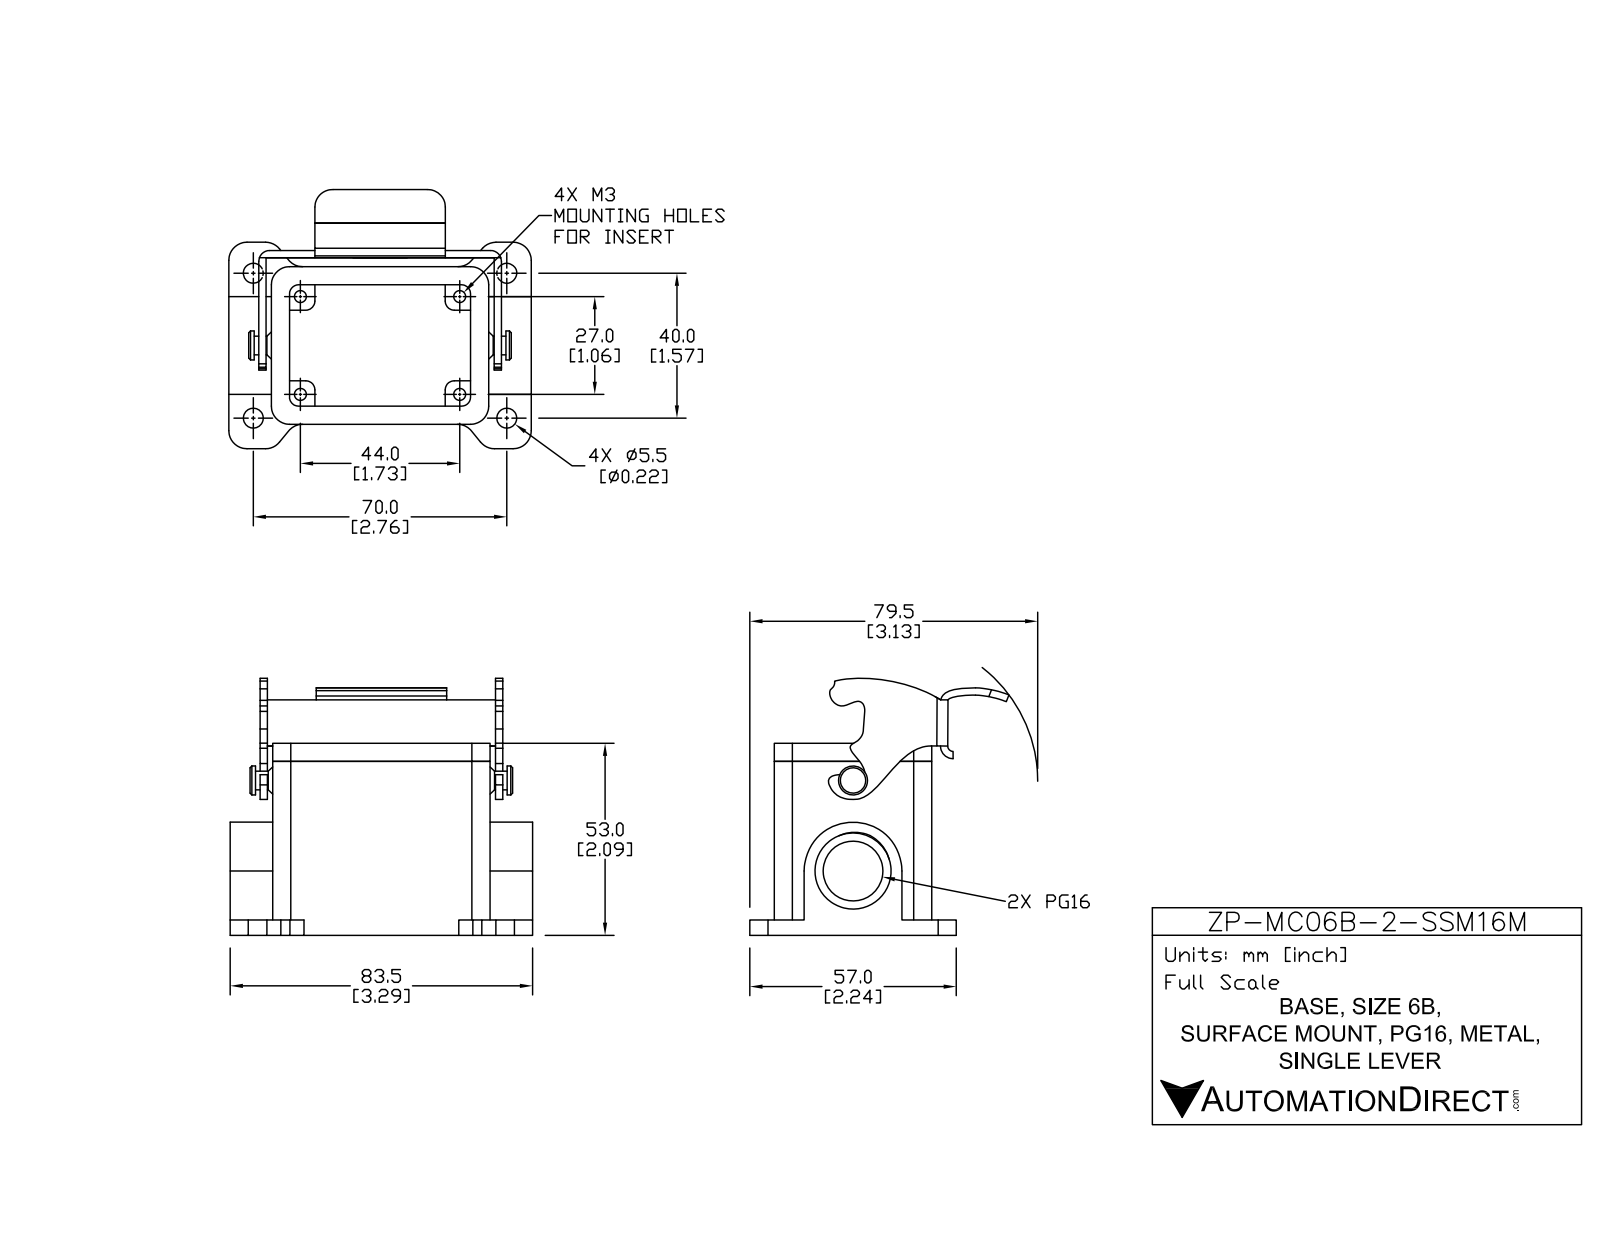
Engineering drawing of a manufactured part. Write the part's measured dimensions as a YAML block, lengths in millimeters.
part_name: "ZP-MC06B-2-SSM16M"
step_written_by: "SolidWorks 2011 (AUTOMOTIVE_DESIGN)"
units: millimeters
bodies: {solids: 3, faces: 239, planar: 89, cylindrical: 130, other: 20}
overall_size: [83.5, 75.97, 65.98]
volume: 76442
surface_area: 36978
round_holes:
  - {diameter: 3.5, count: 4}
  - {diameter: 5.5, count: 4}
  - {diameter: 16.5, count: 1}
  - {diameter: 21, count: 1}
round_bosses_or_shafts:
  - {diameter: 8, count: 1}
  - {diameter: 5.17, count: 1}
partial_cylinders:
  - {radius: 5, count: 17}
  - {radius: 0.13, count: 8}
  - {radius: 0.5, count: 8}
  - {radius: 2.5, count: 8}
  - {radius: 1, count: 4}
  - {radius: 0.59, count: 3}
  - {radius: 2, count: 3}
  - {radius: 4, count: 3}
face_to_face_distances: [5, 38.5, 43.5, 33.5, 1.15, 55, 7, 6.25, 61.25, 12]
hole_center_spacings: [15.07, 15.35, 26, 35.38, 35.93, 40, 43, 50.25]
